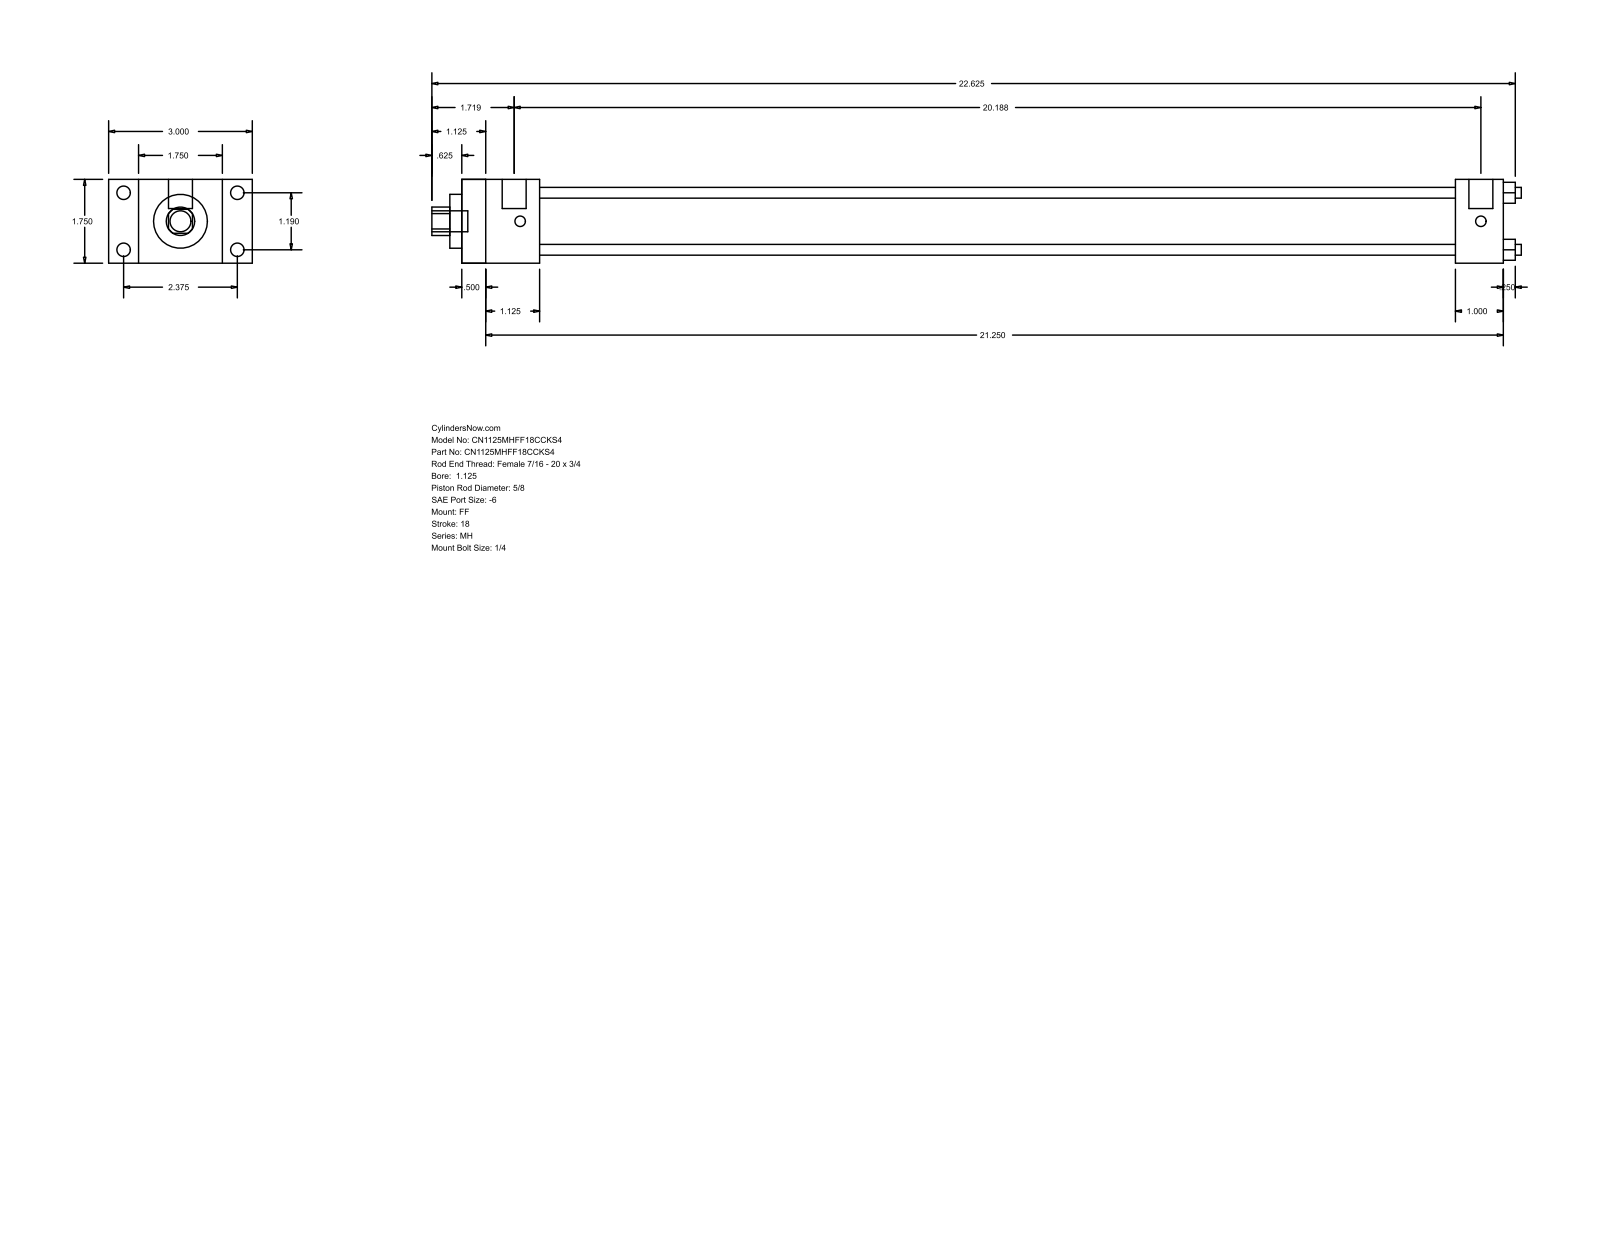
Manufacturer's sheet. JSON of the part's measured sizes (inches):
{"part_name": "MH_FF__0112_0.625", "step_written_by": "GSSL Pune (CONFIG_CONTROL_DESIGN)", "units": "inches", "bodies": {"solids": 0, "faces": 92, "planar": 64, "cylindrical": 28, "other": 0}, "overall_size": [22.75, 3, 1.75], "round_holes": [[0.225, 4], [0.625, 1], [1.125, 1], [1.375, 1]], "round_bosses_or_shafts": [[0.281, 4], [0.219, 4], [0.5, 2], [0.437, 1]], "partial_cylinders_radius": [[0.297, 1]], "face_to_face_distances": [1.75, 21.75, 0.5, 21.25, 0.625, 2.375, 1.125, 1.625, 20.75, 20.25], "hole_center_spacings": [0.841, 1.19, 1.683]}
